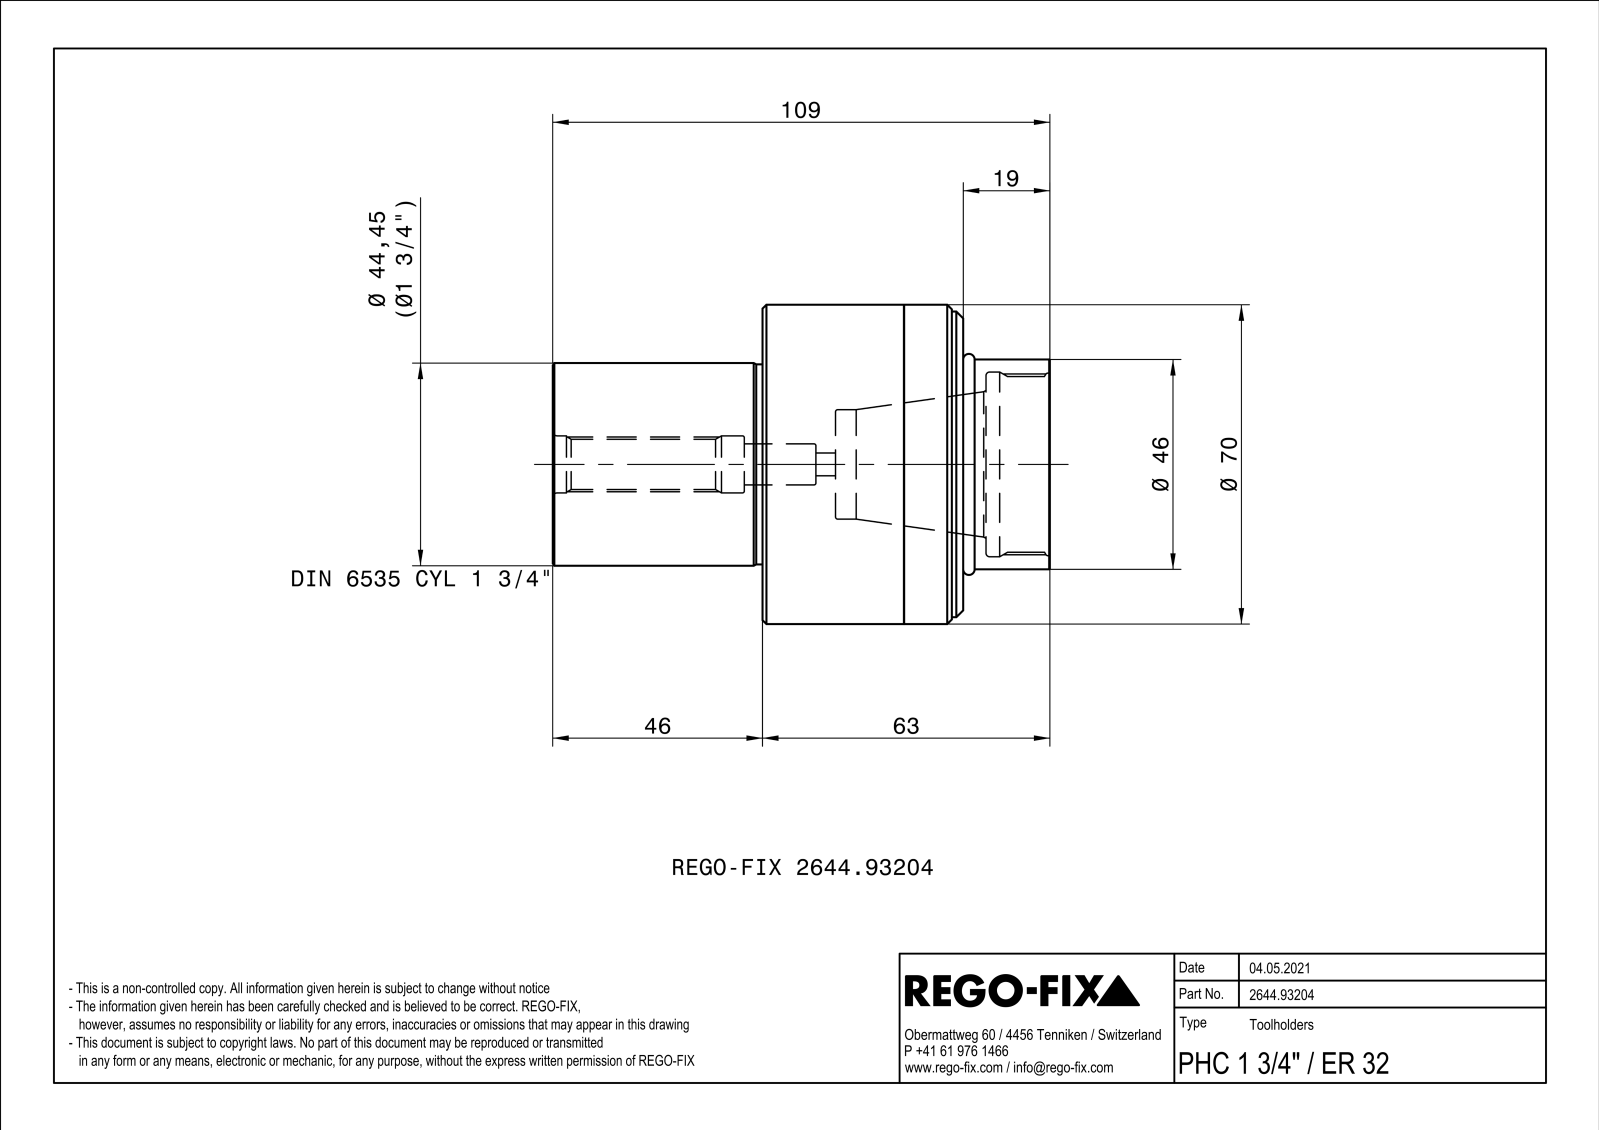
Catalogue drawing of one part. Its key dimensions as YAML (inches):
part_name: "NOCUT"
step_written_by: "SIEMENS PLM Software Solid Edge ST10 (AUTOMOTIVE_DESIGN)"
units: inches
bodies: {solids: 1, faces: 135, planar: 30, cylindrical: 40, other: 65}
overall_size: [4.291, 2.756, 2.756]
volume: 11.73
surface_area: 87.62
round_holes:
  - {diameter: 0.197, count: 4}
  - {diameter: 0.083, count: 1}
  - {diameter: 0.126, count: 1}
  - {diameter: 0.205, count: 1}
  - {diameter: 0.291, count: 1}
  - {diameter: 0.354, count: 1}
  - {diameter: 0.433, count: 1}
  - {diameter: 0.492, count: 1}
  - {diameter: 0.945, count: 1}
  - {diameter: 0.984, count: 1}
  - {diameter: 1.516, count: 1}
  - {diameter: 1.594, count: 1}
round_bosses_or_shafts:
  - {diameter: 2.756, count: 1}
  - {diameter: 2.638, count: 1}
  - {diameter: 2.362, count: 1}
  - {diameter: 2.303, count: 1}
  - {diameter: 2.299, count: 1}
  - {diameter: 2.126, count: 1}
  - {diameter: 2.102, count: 1}
  - {diameter: 1.75, count: 1}
face_to_face_distances: [0.236, 0.224, 0.472, 0.484, 0.248, 1.024, 0.709, 1.26, 1.732, 1.508]
hole_center_spacings: [0.945, 1.336, 1.89, 1.094]
